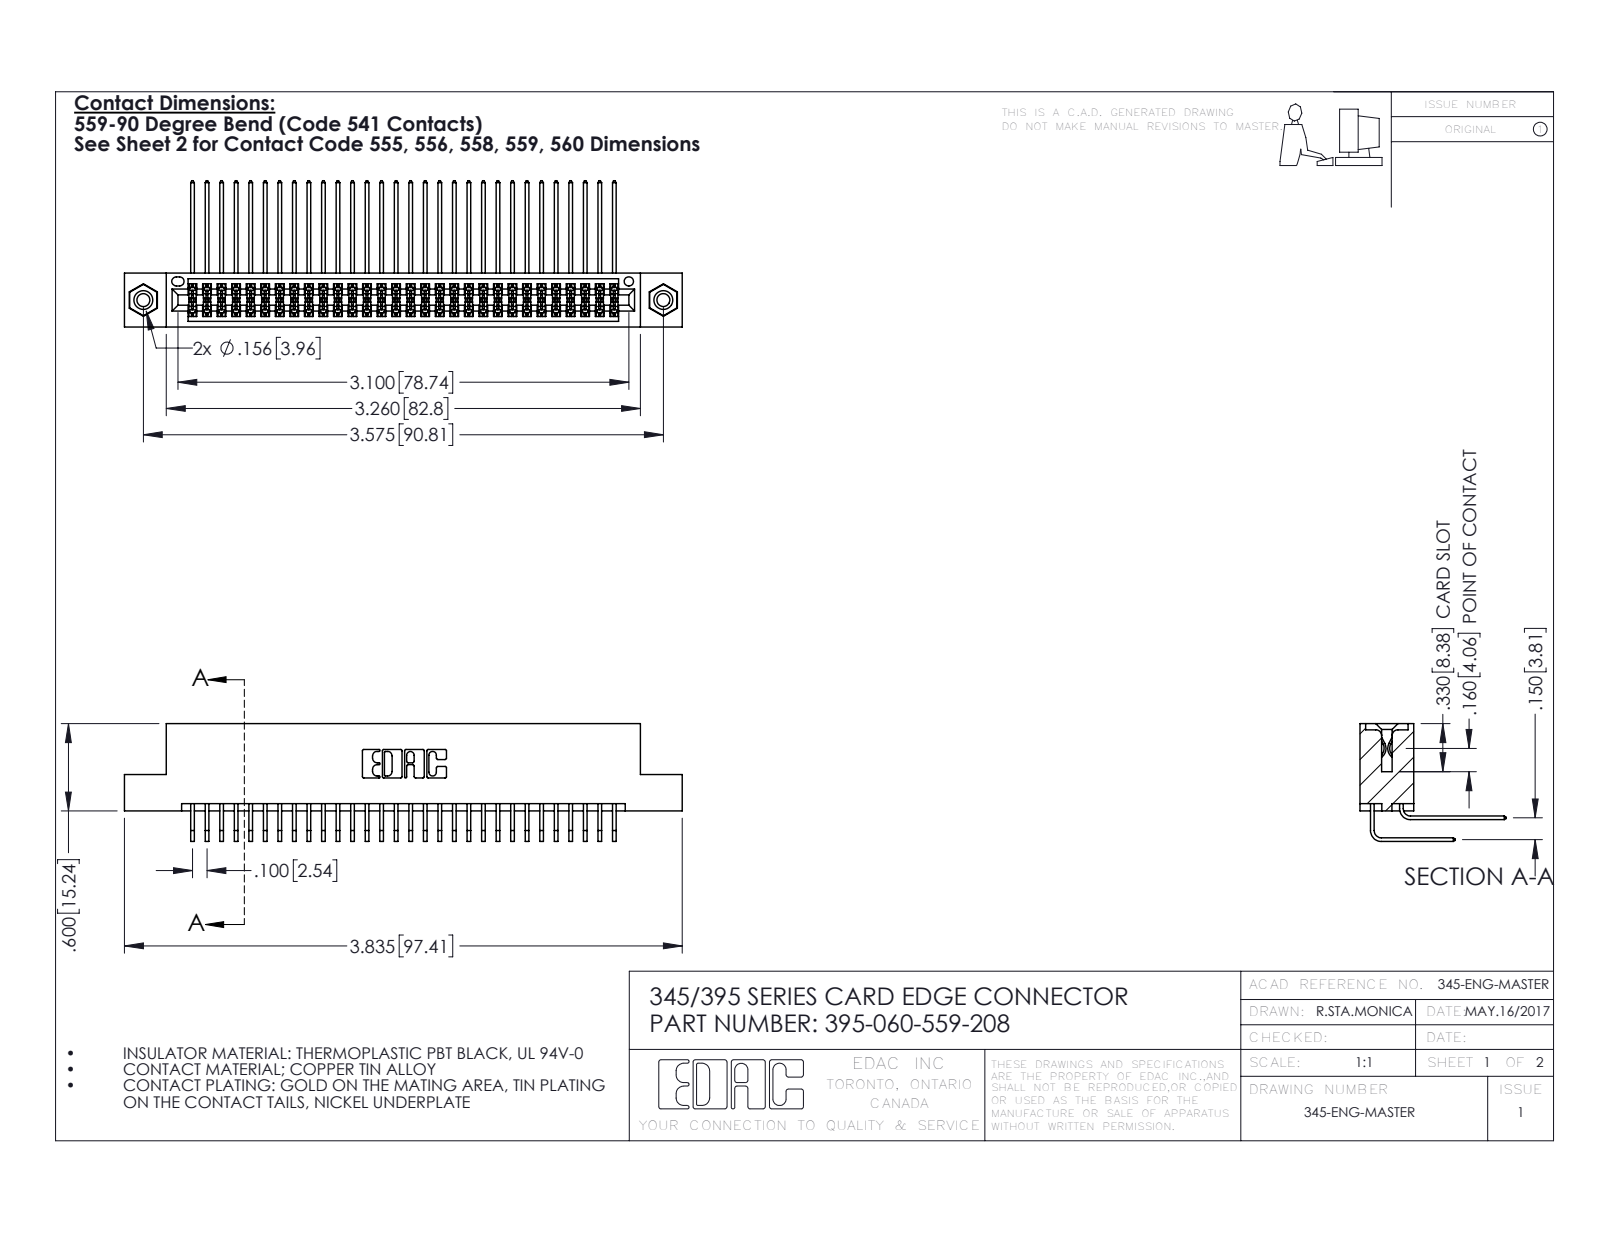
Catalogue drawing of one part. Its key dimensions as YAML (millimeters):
part_name: "395-060-559-208; 345 Part_Flush Mounting Lugs - 0.156 Dia-TI; 345-292-001_559 Tail - 2; 345-250-001_345-250-003-102 (+1 more)"
step_written_by: "SolidWorks 2016 (CONFIG_CONTROL_DESIGN)"
units: millimeters
bodies: {solids: 63, faces: 3306, planar: 2212, cylindrical: 1078, other: 16}
overall_size: [97.4, 25.5, 20.5]
volume: 9680
surface_area: 15740
round_holes:
  - {diameter: 2.3, count: 2}
  - {diameter: 3.2, count: 2}
  - {diameter: 4, count: 2}
  - {diameter: 1.6, count: 1}
round_bosses_or_shafts:
  - {diameter: 3.9, count: 2}
partial_cylinders:
  - {radius: 0.2, count: 90}
  - {radius: 0.3, count: 22}
  - {radius: 0.2, count: 6}
  - {radius: 0.8, count: 6}
  - {radius: 0.7, count: 3}
  - {radius: 0.4, count: 2}
  - {radius: 0.5, count: 2}
  - {radius: 0.6, count: 2}
face_to_face_distances: [1.8, 7.6, 5.1, 9.4, 2.5, 6.9, 0.6, 5.7, 3.8, 4.4]
hole_center_spacings: [6.9, 84.8, 90.8]
